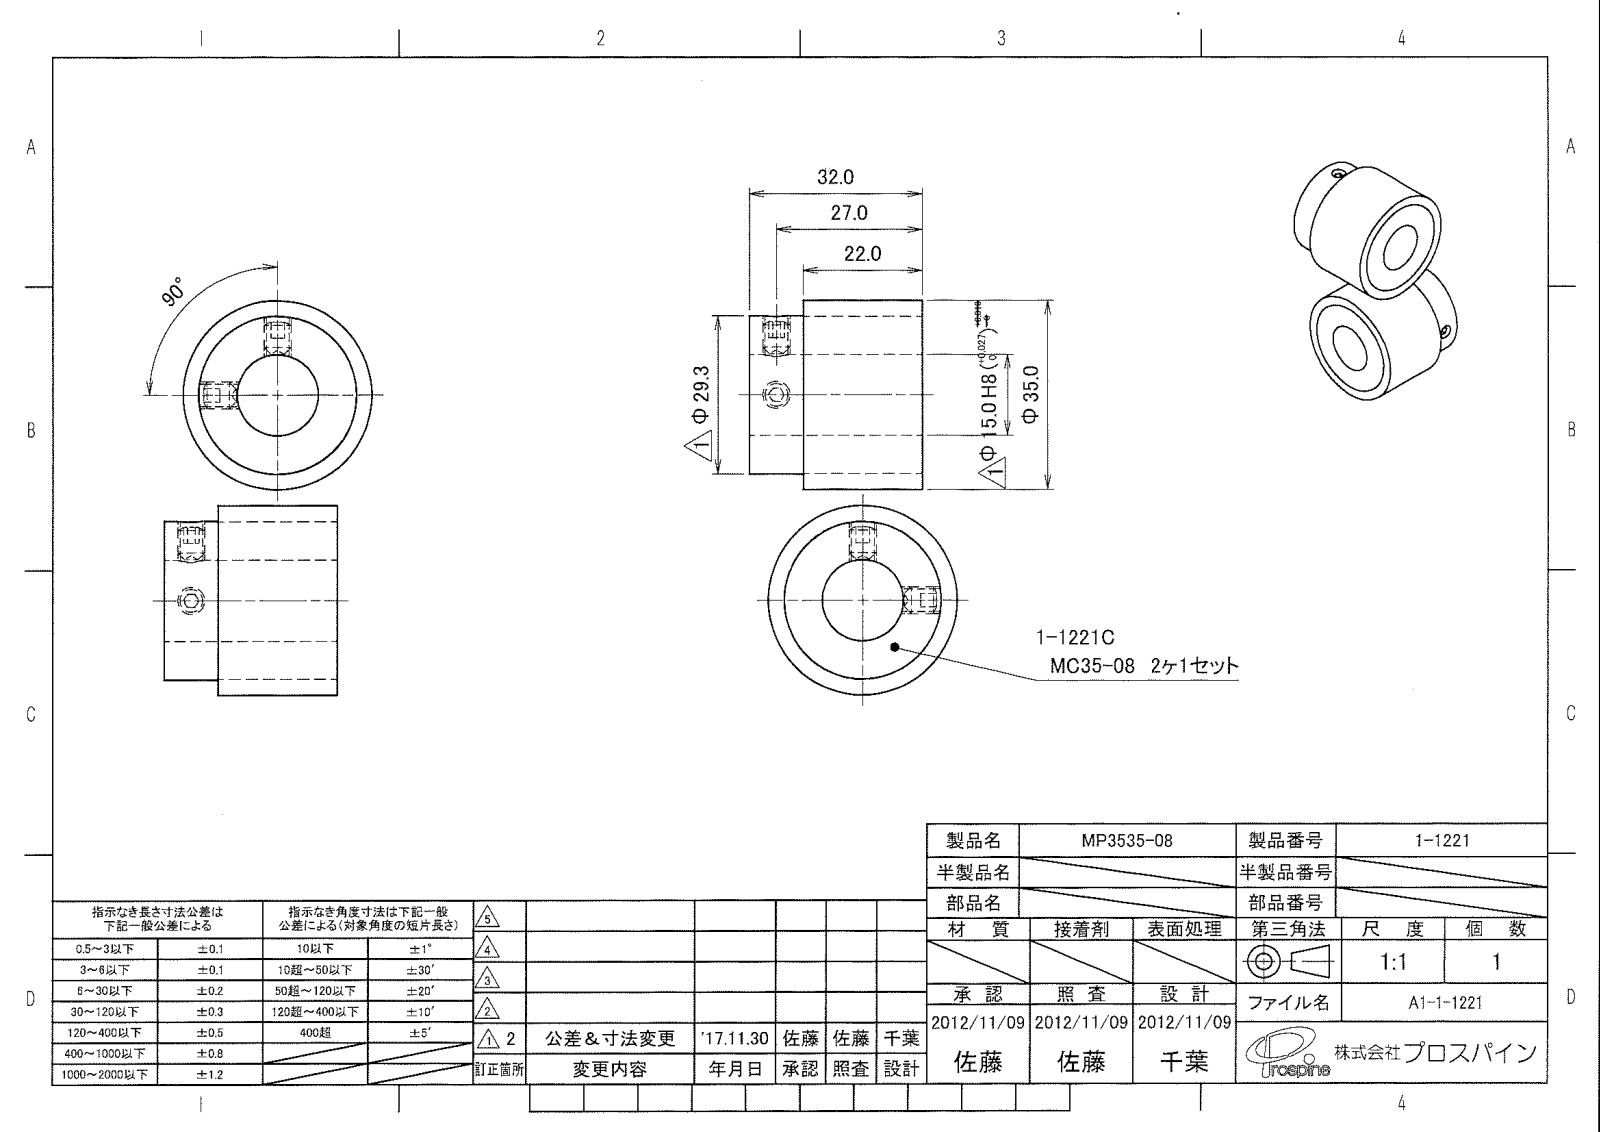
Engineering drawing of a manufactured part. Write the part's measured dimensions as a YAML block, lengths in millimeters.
step_written_by: "PSStep 10.0 (CONFIG_CONTROL_DESIGN)"
units: millimeters
bodies: {solids: 6, faces: 56, planar: 33, cylindrical: 11, other: 12}
overall_size: [35, 35, 32]
volume: 22395
surface_area: 11147
round_holes:
  - {diameter: 4.2, count: 2}
  - {diameter: 15, count: 1}
  - {diameter: 29.1, count: 1}
round_bosses_or_shafts:
  - {diameter: 5, count: 2}
  - {diameter: 35, count: 1}
  - {diameter: 29.3, count: 1}
face_to_face_distances: [32, 10, 22, 2.5, 11.85, 9.46, 9.35, 11.96]
